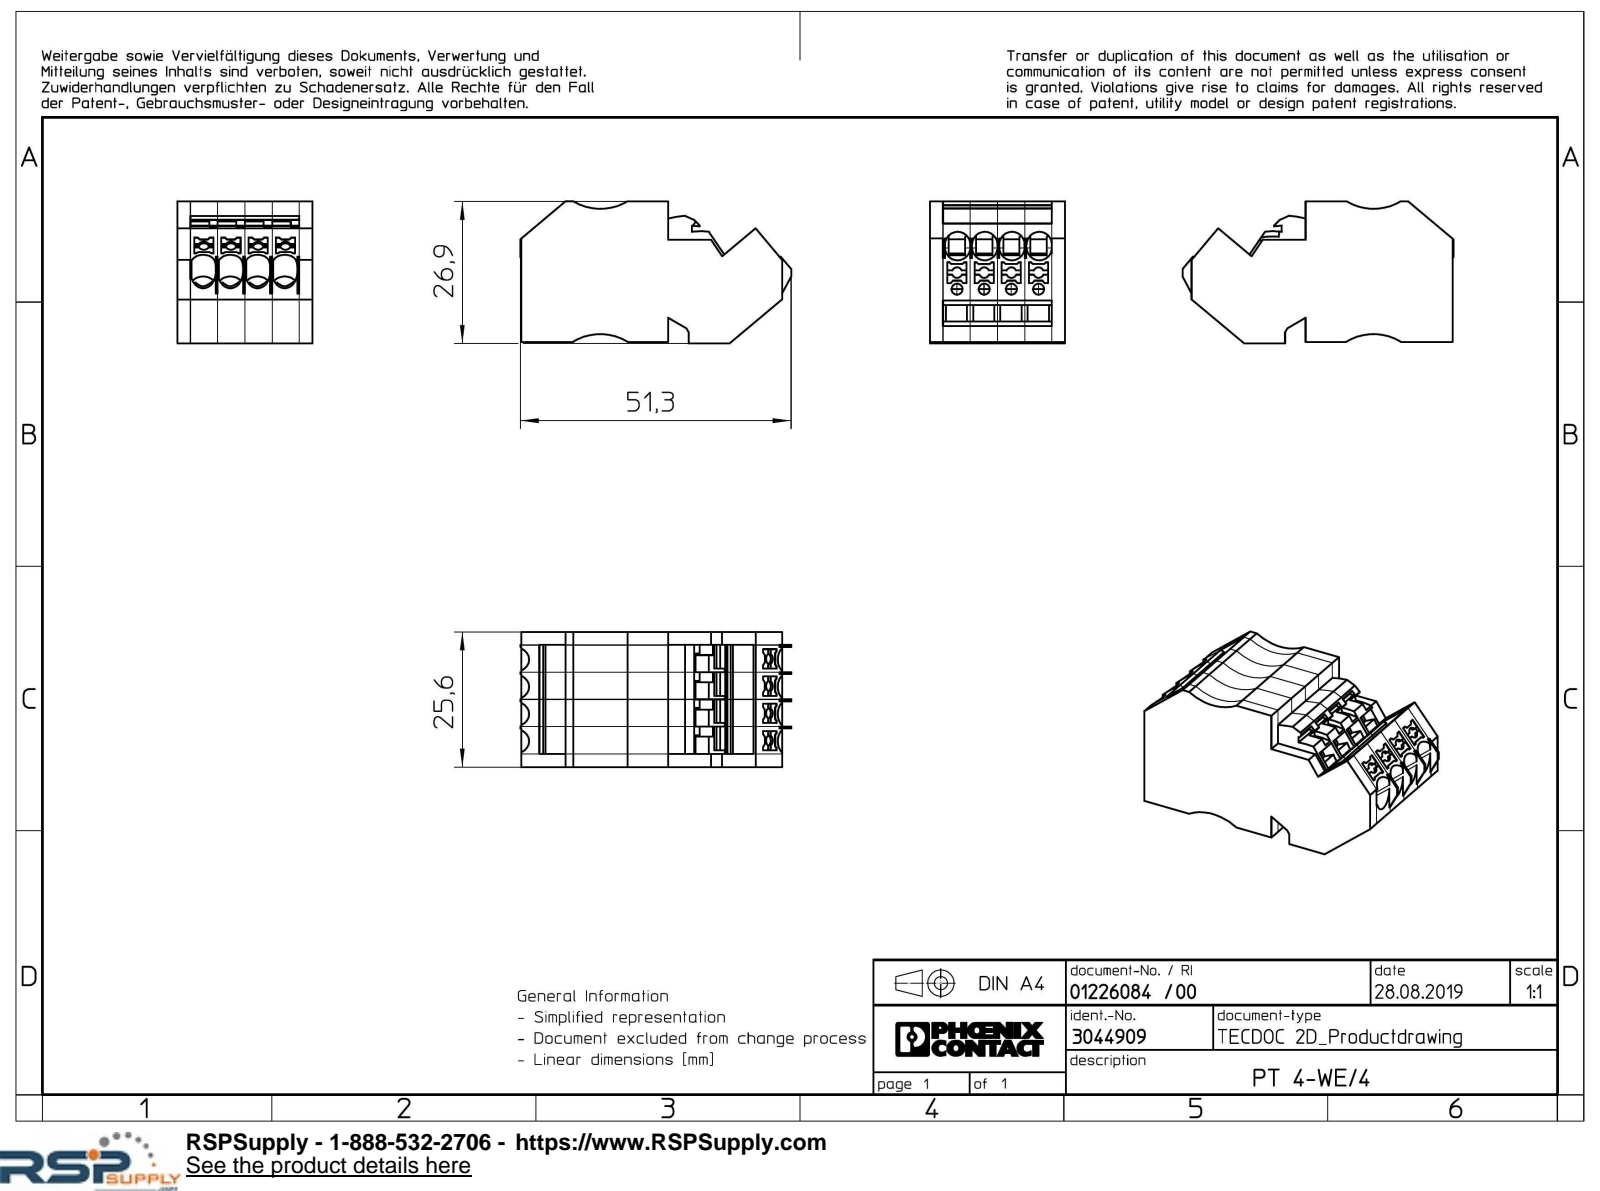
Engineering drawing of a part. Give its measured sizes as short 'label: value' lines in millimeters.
name: PT_4_WE_4-select
written by: Creo Elements/Direct Modeling 20.1A 29-Sep-2018 (C) Parametric Technology GmbH (AUTOMOTIVE_DESIGN)
unit: mm
bodies: 1 solid, 707 faces (615 planar, 84 cylindrical, 8 other)
size: 51.3 × 26.9 × 25.6
volume: 23 591 mm³; area: 9 822 mm²
holes: 4× ⌀2.1
rounds: 16× R2.4, 8× R1, 3× R1.03, 2× R10, 1× R1.05, 1× R1.78, 1× R12.4, 1× R13.38
face distances: 25.6, 5.15, 10.3, 15.45, 3.15, 3.85, 7, 19.6, 3.1, 7.3
hole spacings: 5.15, 10.3, 15.45
